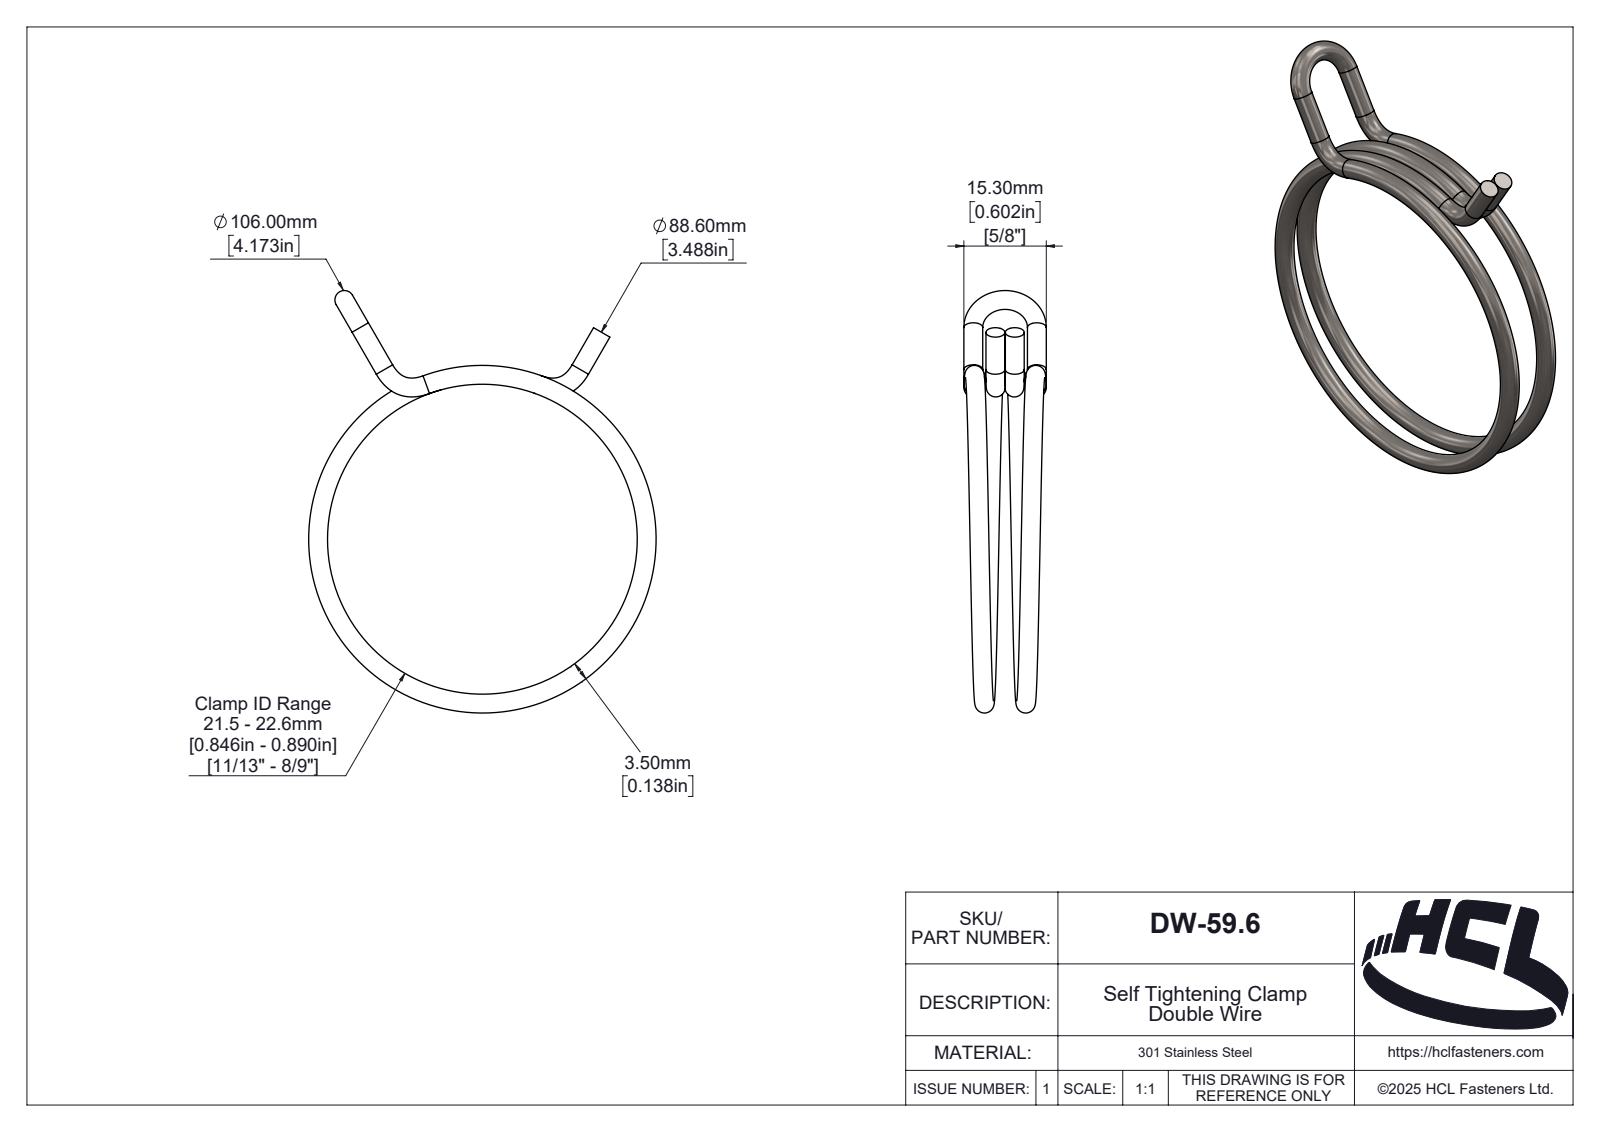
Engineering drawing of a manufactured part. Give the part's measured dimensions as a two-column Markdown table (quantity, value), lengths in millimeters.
| quantity | value |
| --- | --- |
| part name | DW-59.6 |
| STEP written by | SolidWorks 2025 (AUTOMOTIVE_DESIGN) |
| units | millimeters |
| bodies | 1 solid, 132 faces (14 planar, 53 cylindrical, 65 other) |
| overall size | 78.38 × 64.49 × 15.3 |
| volume | 4 953 mm³ |
| surface area | 5 676 mm² |
| round bosses / shafts (diameter × count) | 3.5 × 4 |
| partial cylindrical surfaces (radius × count) | 0.16 × 1, 0.2 × 1, 0.21 × 1, 0.26 × 1, 0.36 × 1, 0.48 × 1, 0.6 × 1, 0.68 × 1 |
